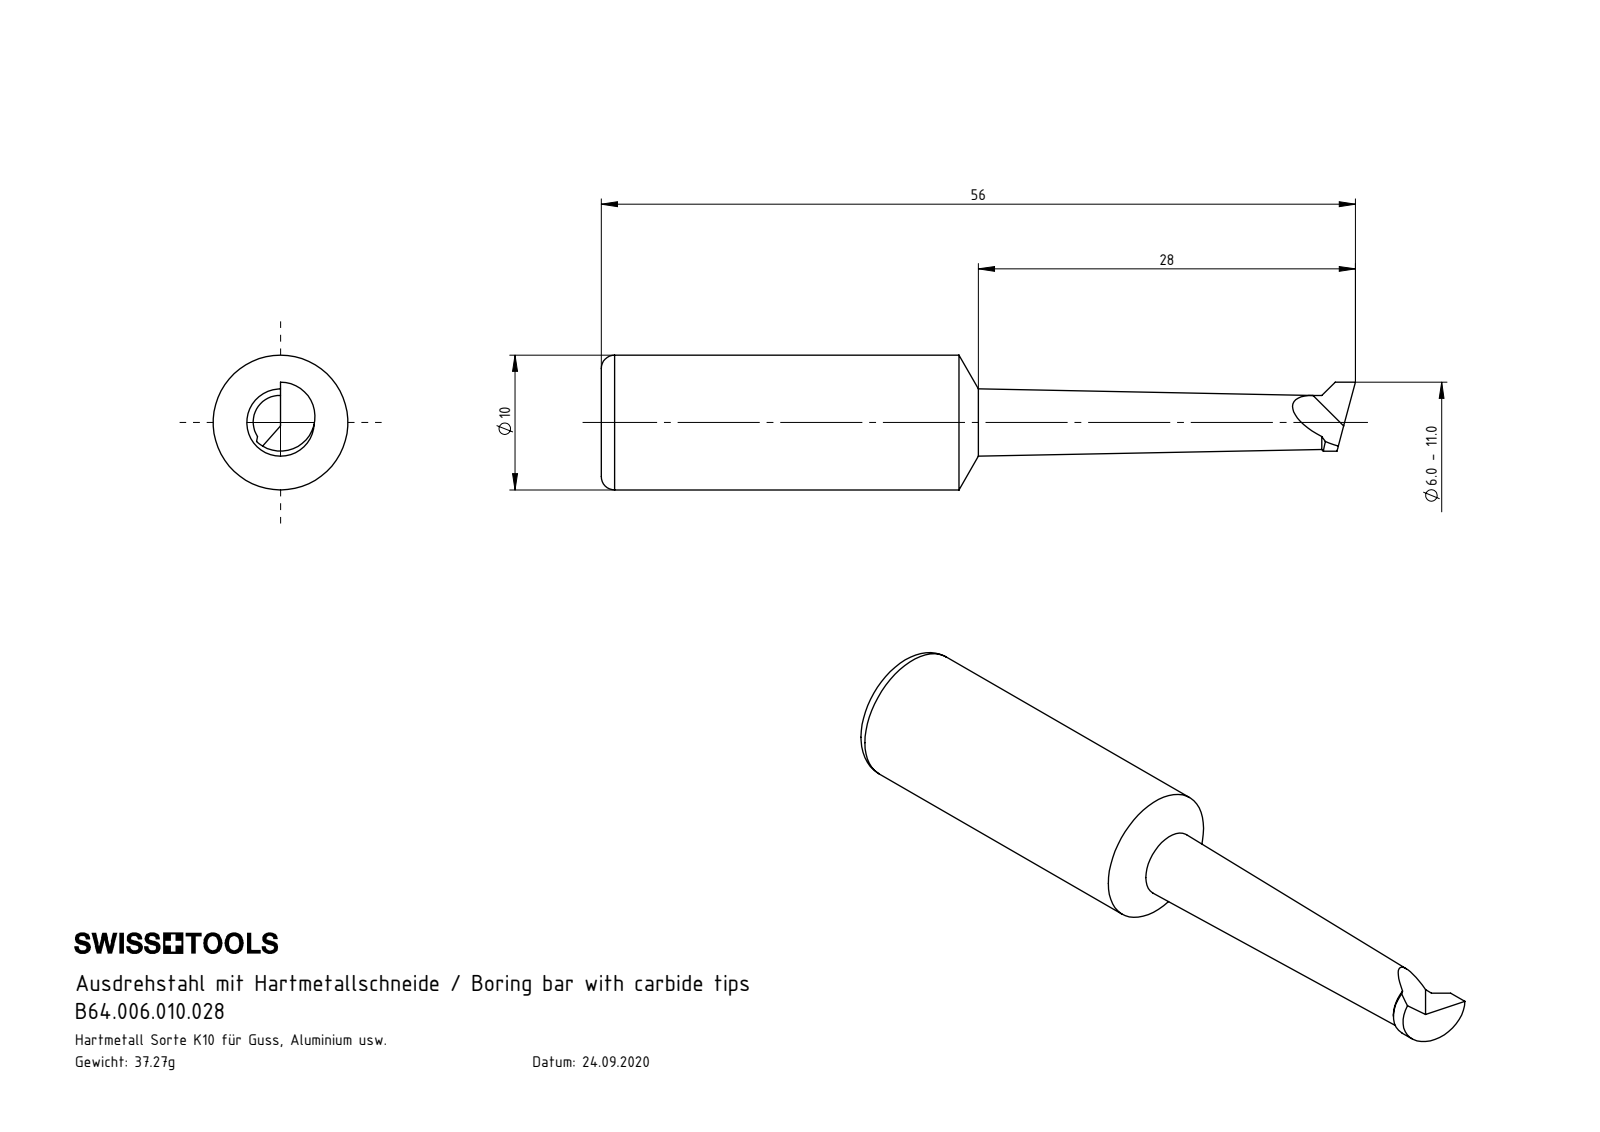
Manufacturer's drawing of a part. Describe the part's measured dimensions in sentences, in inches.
The part is named "B64.006.010.028". Its 3-D file was written by "SolidWorks 2022 (CONFIG_CONTROL_DESIGN)". It is 1 solid with 14 faces: 4 planar, 3 cylindrical and 7 other. Overall it measures 2.205 by 0.394 by 0.394 inches. Its volume is 0.157 cubic inches and its surface area 2.119 square inches. Round bosses or shafts: 1 of diameter 0.394. Partial cylindrical surfaces (rounded edges, fillets, slot ends): 1 of radius 0.101.
